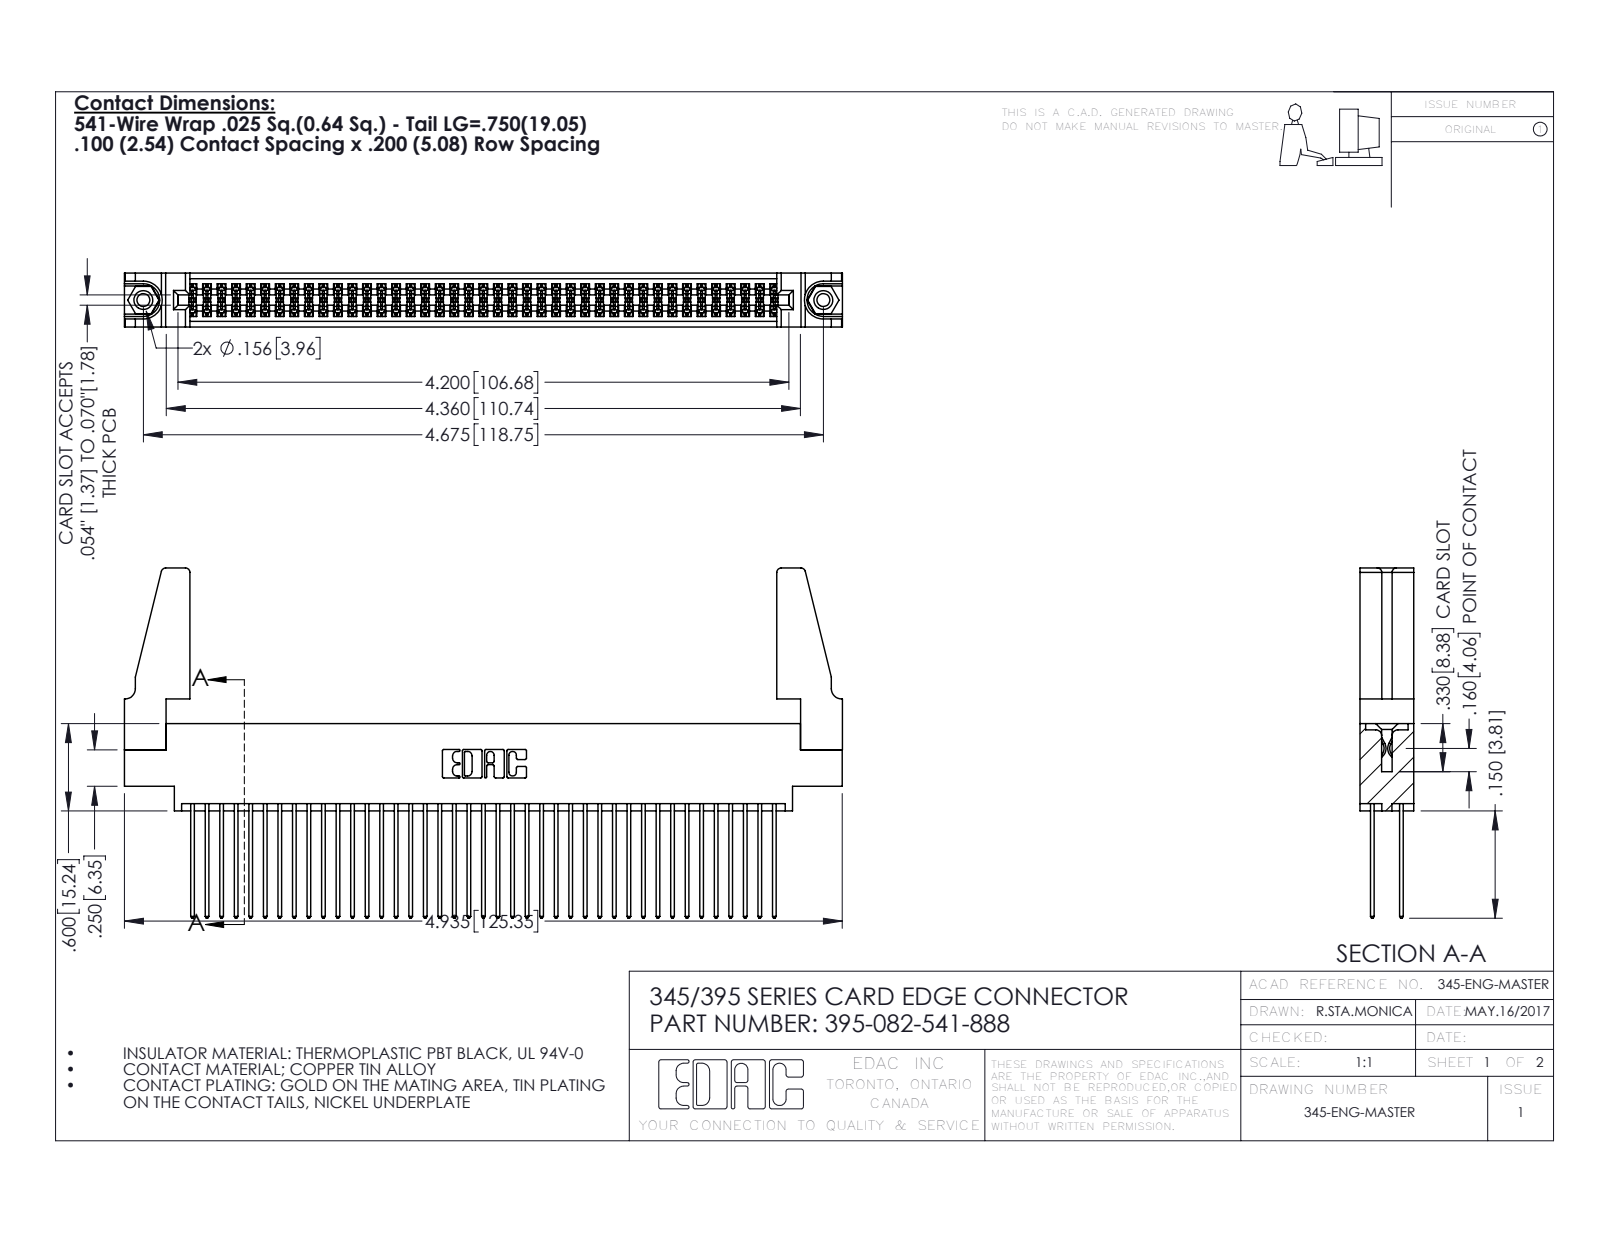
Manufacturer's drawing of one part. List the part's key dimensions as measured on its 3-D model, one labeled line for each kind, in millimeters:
Part name (STEP PRODUCT): 345 Part_0.170 Offset - 0.156 Dia-TH; 395-082-541-888; 345-292-001_345-293-141; 345-220-078_345-220-088 (+1 more)
STEP written by: SolidWorks 2016 (CONFIG_CONTROL_DESIGN)
Units: millimetres
Bodies: 87 solids, 4354 faces (2862 planar, 1476 cylindrical, 16 other)
Overall size (bounding box): 125.4 × 61.1 × 9.4
Volume: 15 800 mm³ · Surface area: 23 970 mm²
Round holes (diameter × count): ⌀2.3 ×2, ⌀3.2 ×2, ⌀4 ×2, ⌀1.6 ×1
Round bosses / shafts (diameter × count): ⌀3.9 ×2
Partial cylindrical surfaces — rounded edges, fillets, slot ends (radius × count): R0.2 ×123, R0.3 ×82, R0.3 ×22, R0.8 ×8, R0.2 ×6, R0.8 ×6, R0.7 ×3, R0.4 ×2
Main face-to-face distances: 1.8, 7.6, 5.1, 2.5, 6.9, 0.6, 9.4, 5.7, 4.4, 3.8
Hole centre spacings: 6.9, 112.8, 118.7
